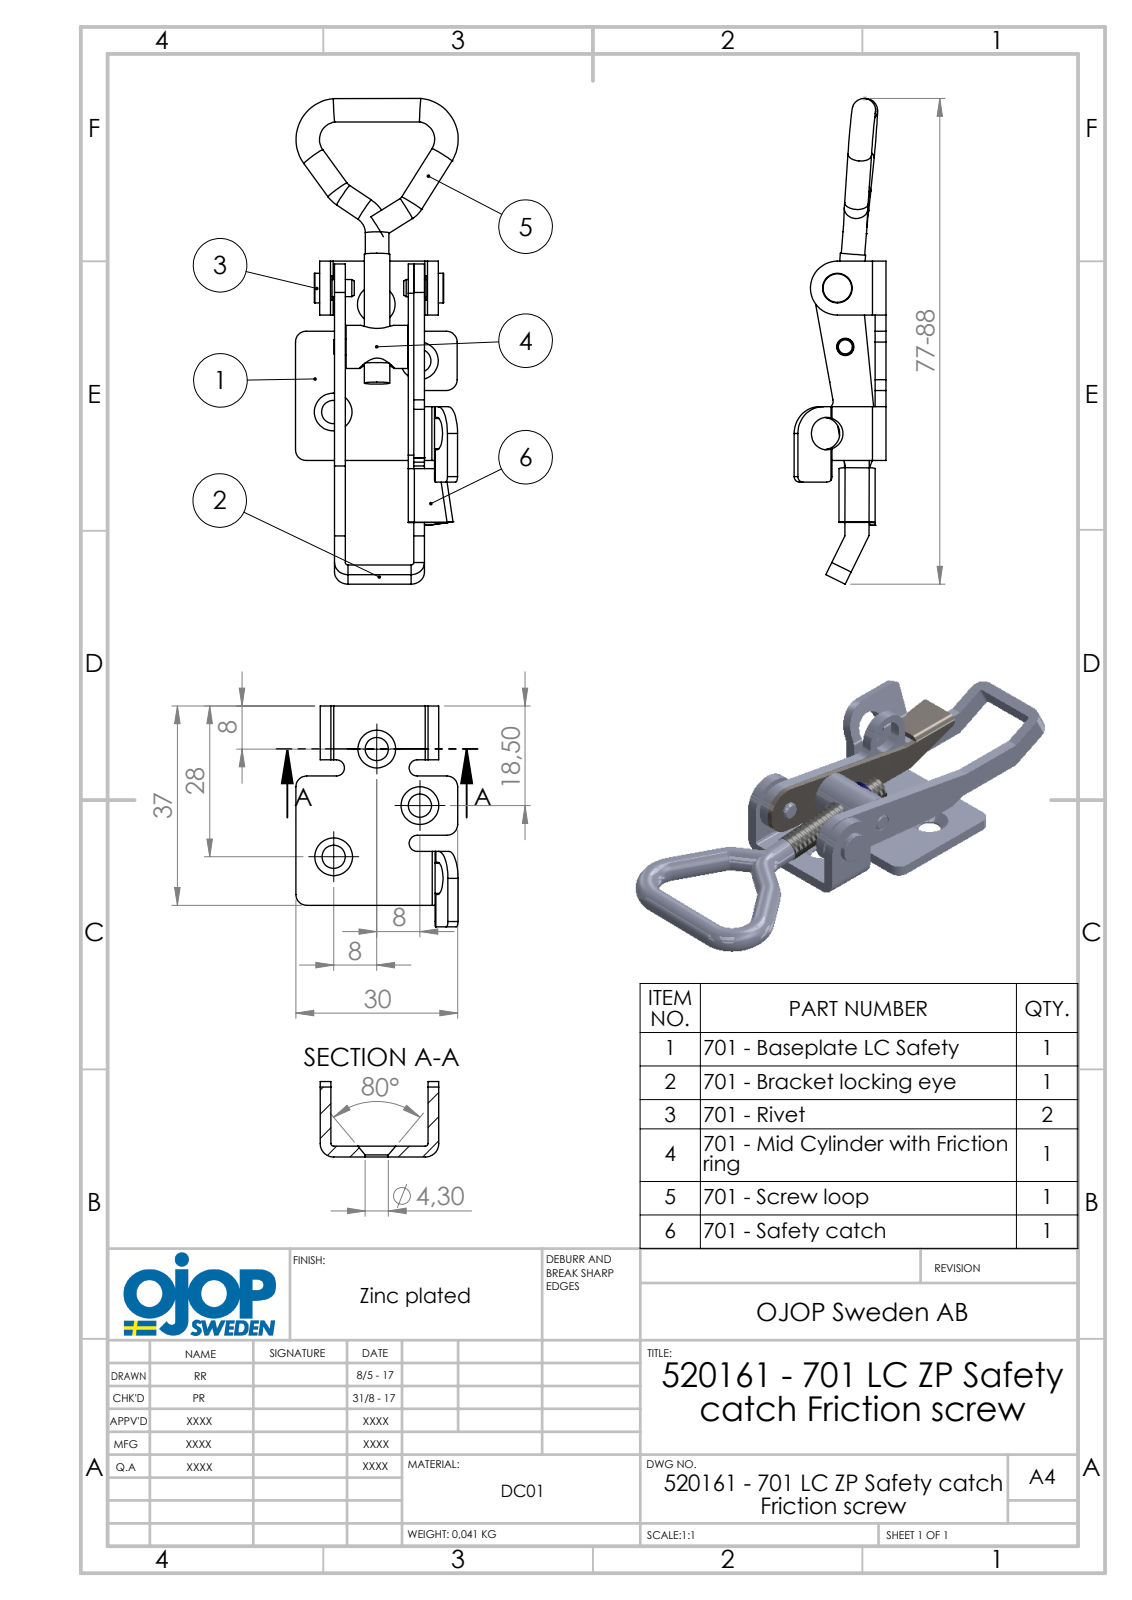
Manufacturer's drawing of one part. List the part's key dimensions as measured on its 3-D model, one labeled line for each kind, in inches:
Part name (STEP PRODUCT): 520161 - 701 LC ZP Safety catch Friction screw; 701 - LC Safety; 701 - Bygel Låsögla; 701 - Ansatsnit (+5 more)
STEP written by: SolidWorks 2015 (AUTOMOTIVE_DESIGN)
Units: inches
Bodies: 8 solids, 253 faces (112 planar, 105 cylindrical, 36 other)
Overall size (bounding box): 3.55 × 1.189 × 0.67
Volume: 0.406 in³ · Surface area: 13.44 in²
Round holes (diameter × count): ⌀0.169 ×5, ⌀0.126 ×2, ⌀0.177 ×1, ⌀0.236 ×1, ⌀0.256 ×1
Round bosses / shafts (diameter × count): ⌀0.172 ×5, ⌀0.315 ×1, ⌀0.256 ×1, ⌀0.217 ×1, ⌀0.185 ×1, ⌀0.124 ×1, ⌀0.118 ×1
Partial cylindrical surfaces — rounded edges, fillets, slot ends (radius × count): R0.02 ×7, R0.098 ×6, R0.059 ×5, R0.079 ×4, R0.004 ×3, R0.043 ×3, R0.039 ×2, R0.177 ×2
Main face-to-face distances: 0.079, 0.579, 0.039, 0.118, 0.5, 0.657, 0.461, 0.539, 0.687, 0.1
Hole centre spacings: 0.433, 0.52, 0.653, 0.733, 0.848, 1.067
